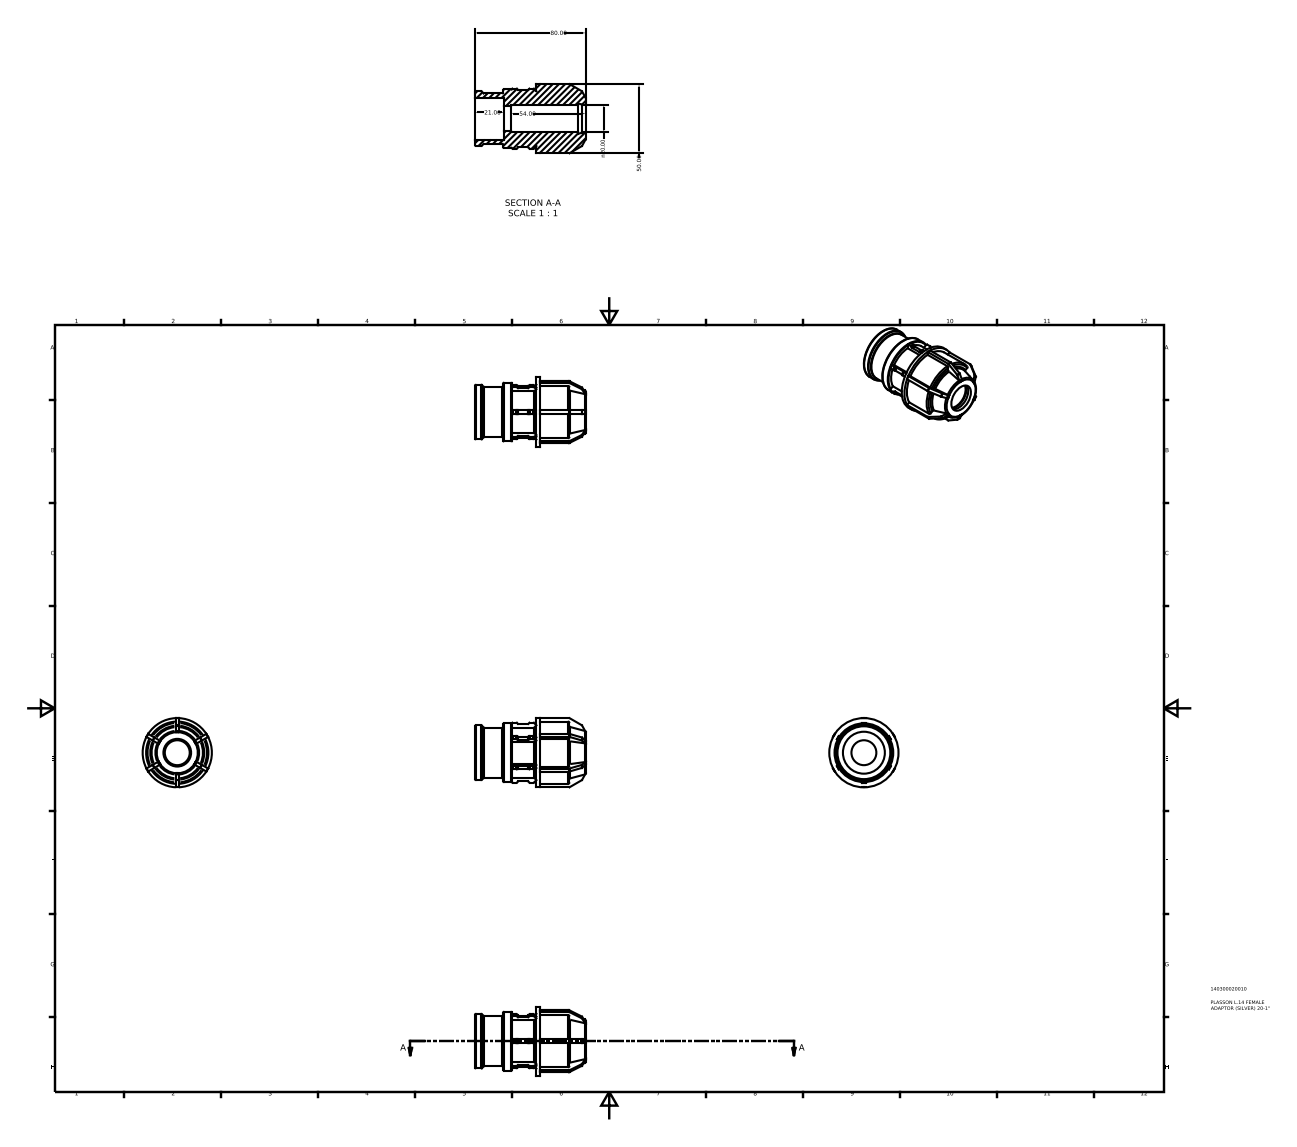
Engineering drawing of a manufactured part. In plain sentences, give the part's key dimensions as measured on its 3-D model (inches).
The part is named "140300020010". Its 3-D file was written by "Autodesk Inventor 2015 (AUTOMOTIVE_DESIGN)". It is 1 solid with 261 faces: 159 planar, 68 cylindrical and 34 other. Overall it measures 3.15 by 1.969 by 1.969 inches. Its volume is 4.164 cubic inches and its surface area 32.96 square inches. Round holes: 1 of diameter 0.709, 1 of diameter 0.787, 1 of diameter 1.193. Round bosses or shafts: 1 of diameter 1.969, 1 of diameter 1.772, 1 of diameter 1.67, 1 of diameter 1.55, 1 of diameter 1.431. Partial cylindrical surfaces (rounded edges, fillets, slot ends): 48 of radius 0.024. The main face-to-face distances are 0.098, 0.92, 0.827, 1.746, 3.15, 2.323, 1.403, 0.106, 1.297, 0.222.
